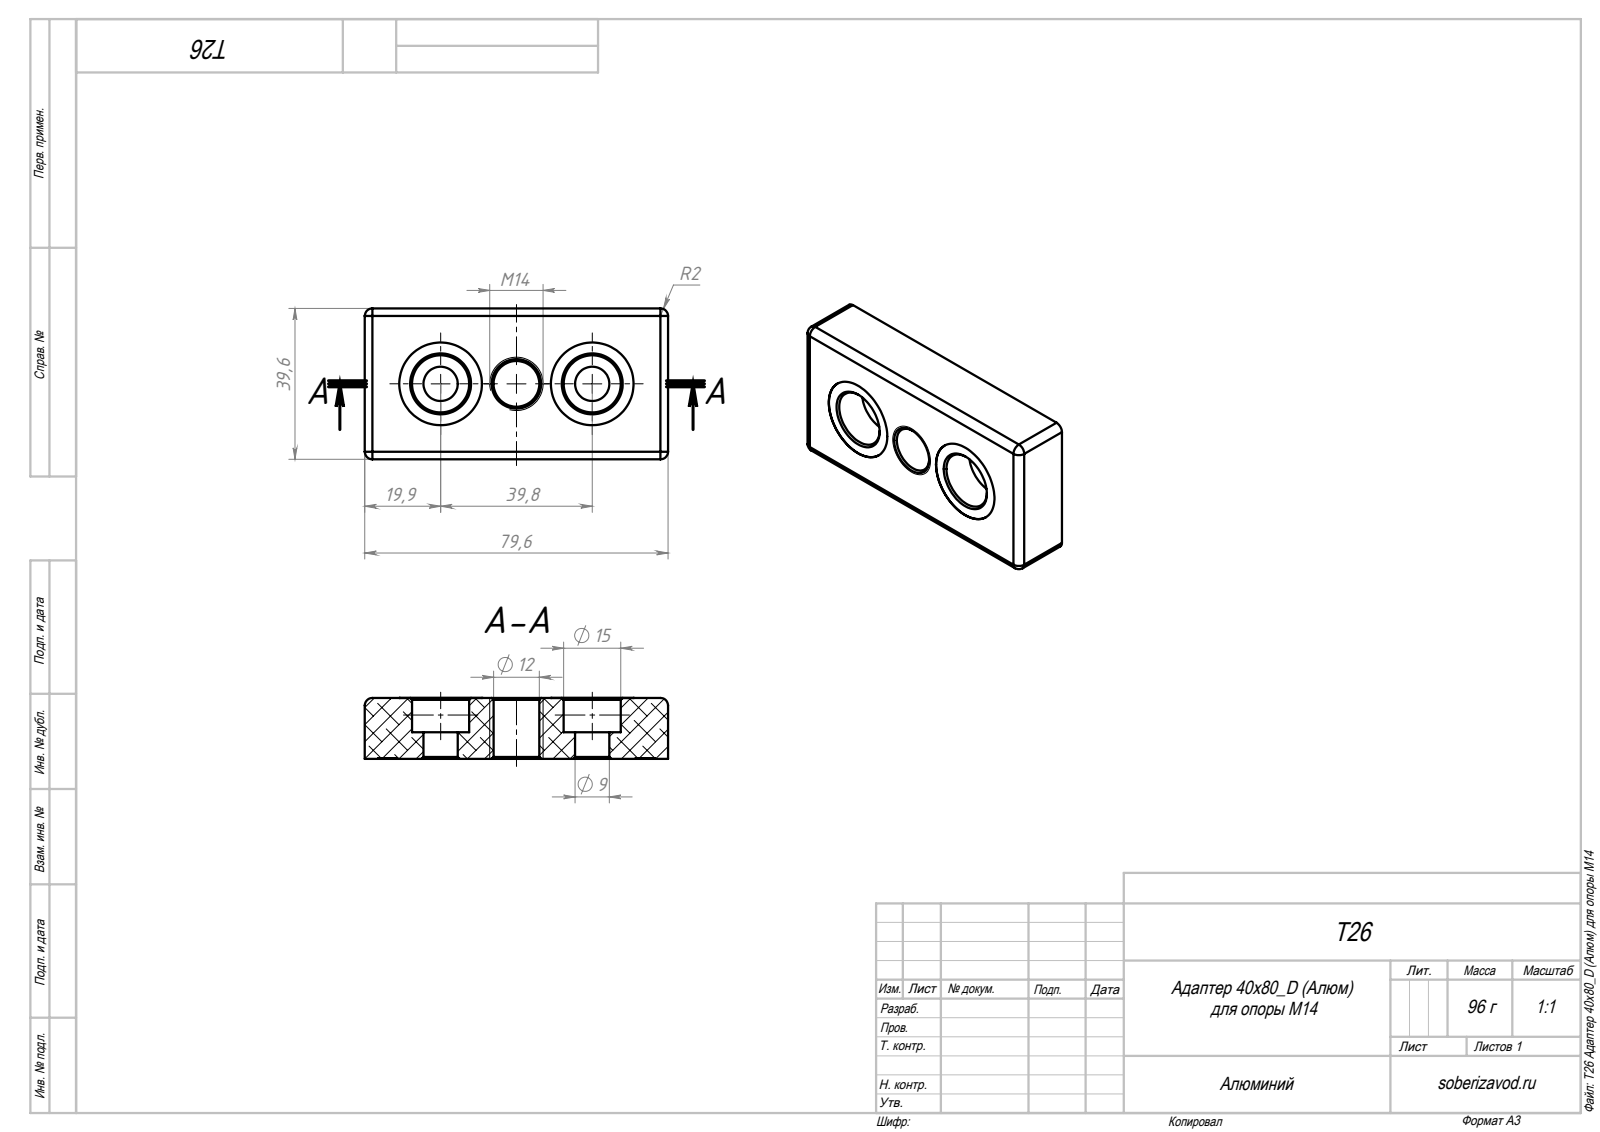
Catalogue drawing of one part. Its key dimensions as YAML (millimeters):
step_written_by: "SolidWorks 2018 (AUTOMOTIVE_DESIGN)"
units: millimeters
bodies: {solids: 1, faces: 166, planar: 50, cylindrical: 100, other: 16}
overall_size: [79.6, 39.6, 16]
volume: 35563
surface_area: 15575
round_holes:
  - {diameter: 5, count: 4}
  - {diameter: 9, count: 2}
  - {diameter: 15, count: 2}
  - {diameter: 21.7, count: 2}
  - {diameter: 12, count: 1}
round_bosses_or_shafts:
  - {diameter: 5, count: 4}
partial_cylinders:
  - {radius: 0.5, count: 24}
  - {radius: 1, count: 8}
  - {radius: 2, count: 8}
  - {radius: 13.9, count: 2}
  - {radius: 15.9, count: 1}
face_to_face_distances: [3, 16, 36.6, 39.6, 76.6, 33.6, 13, 79.6, 73.6, 15.98]
hole_center_spacings: [13.9, 24.27, 36.55, 19.9, 33.8, 53.7, 27.8, 39.8]
